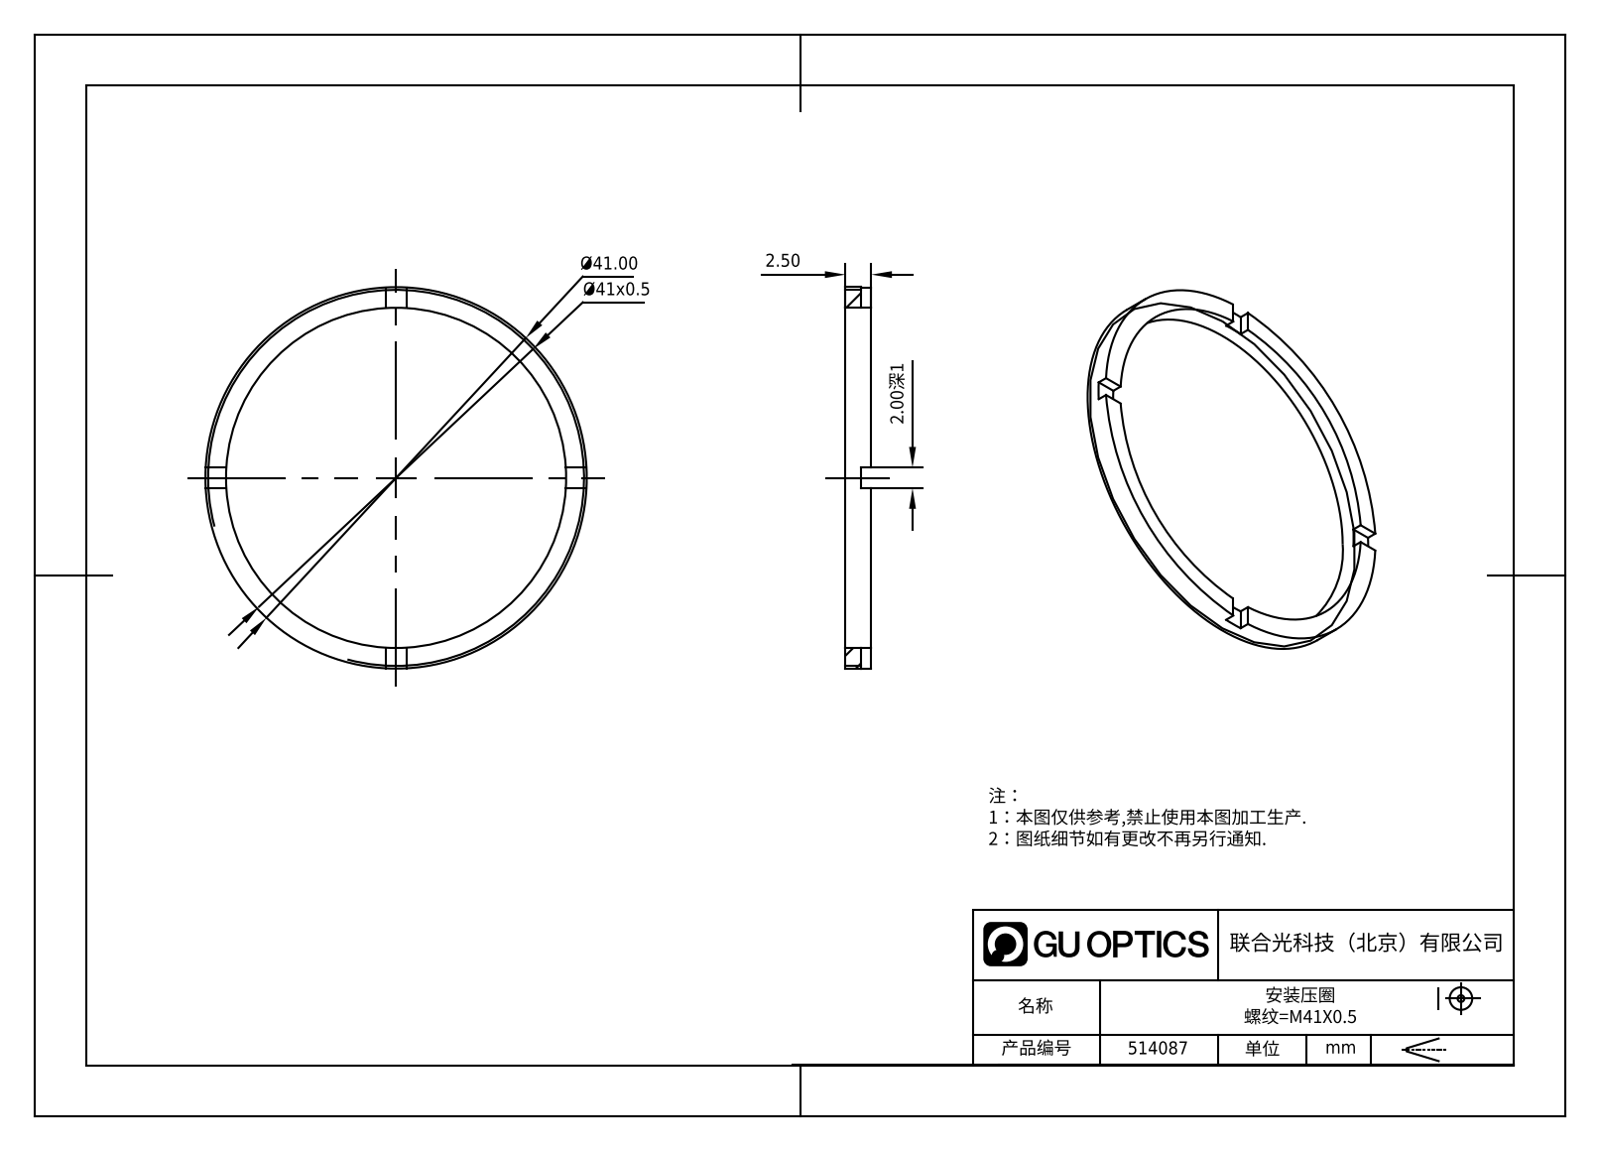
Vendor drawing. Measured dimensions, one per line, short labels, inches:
name: 514087
written by: SolidWorks 2020 (CONFIG_CONTROL_DESIGN)
unit: in
bodies: 1 solid, 21 faces (17 planar, 4 cylindrical, 0 other)
size: 1.614 × 1.614 × 0.098
volume: 0.036 in³; area: 1.71 in²
holes: 1× ⌀1.457
bosses: 1× ⌀1.614
face distances: 0.098, 0.059, 0.039, 0.079
